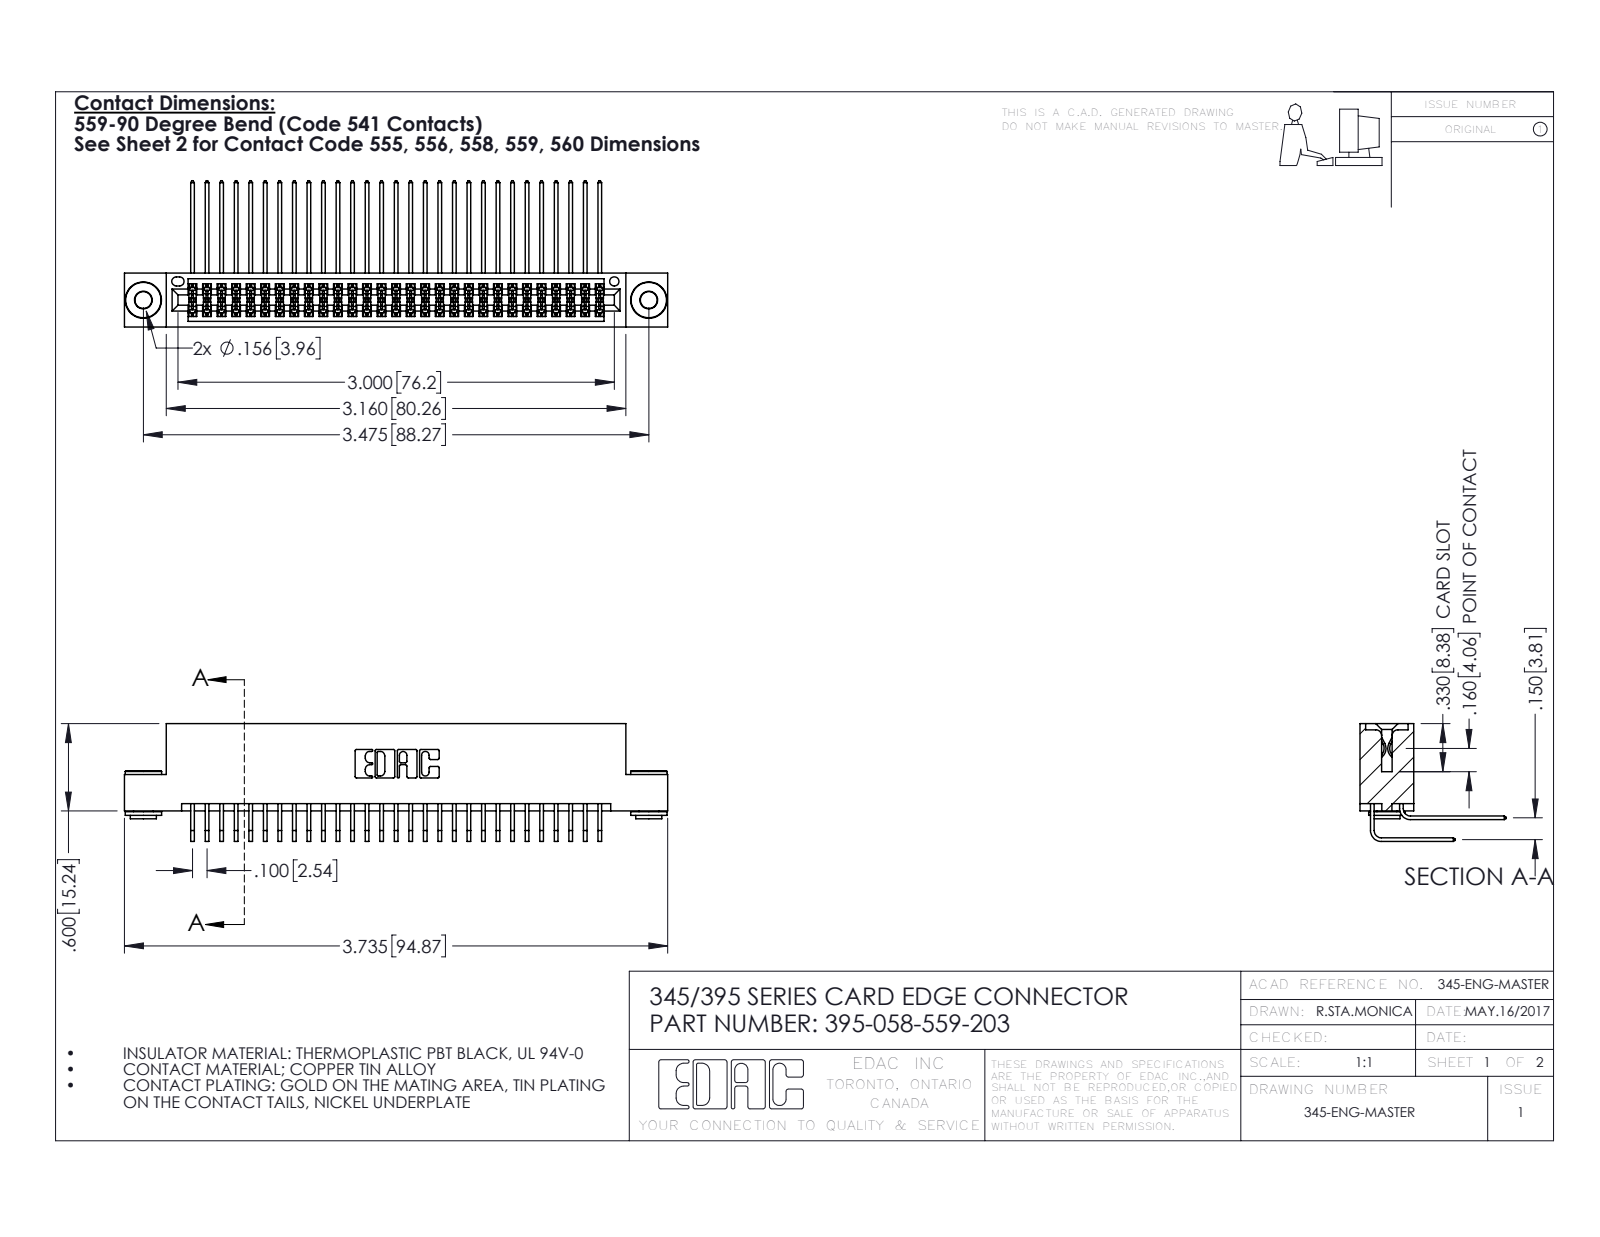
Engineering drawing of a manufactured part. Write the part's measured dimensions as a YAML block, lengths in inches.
part_name: "345-292-001_559 Tail - 2; 395-058-559-203; 345-292-001_558 559 Tail - 1; 345 Part_Flush Mounting Lugs - 0.156 Dia-TH (+1 more)"
step_written_by: "SolidWorks 2016 (CONFIG_CONTROL_DESIGN)"
units: inches
bodies: {solids: 61, faces: 3180, planar: 2120, cylindrical: 1052, other: 8}
overall_size: [3.735, 1.005, 0.809]
volume: 0.577
surface_area: 24.02
round_holes:
  - {diameter: 0.116, count: 2}
  - {diameter: 0.156, count: 2}
  - {diameter: 0.064, count: 1}
round_bosses_or_shafts:
  - {diameter: 0.25, count: 2}
  - {diameter: 0.18, count: 2}
  - {diameter: 0.136, count: 2}
partial_cylinders:
  - {radius: 0.006, count: 88}
  - {radius: 0.01, count: 22}
  - {radius: 0.007, count: 6}
  - {radius: 0.031, count: 6}
  - {radius: 0.026, count: 3}
  - {radius: 0.014, count: 2}
  - {radius: 0.019, count: 2}
  - {radius: 0.022, count: 2}
face_to_face_distances: [0.072, 0.298, 0.2, 0.37, 0.025, 0.098, 0.272, 0.225, 0.15, 0.175]
hole_center_spacings: [0.27, 3.24, 3.475]
